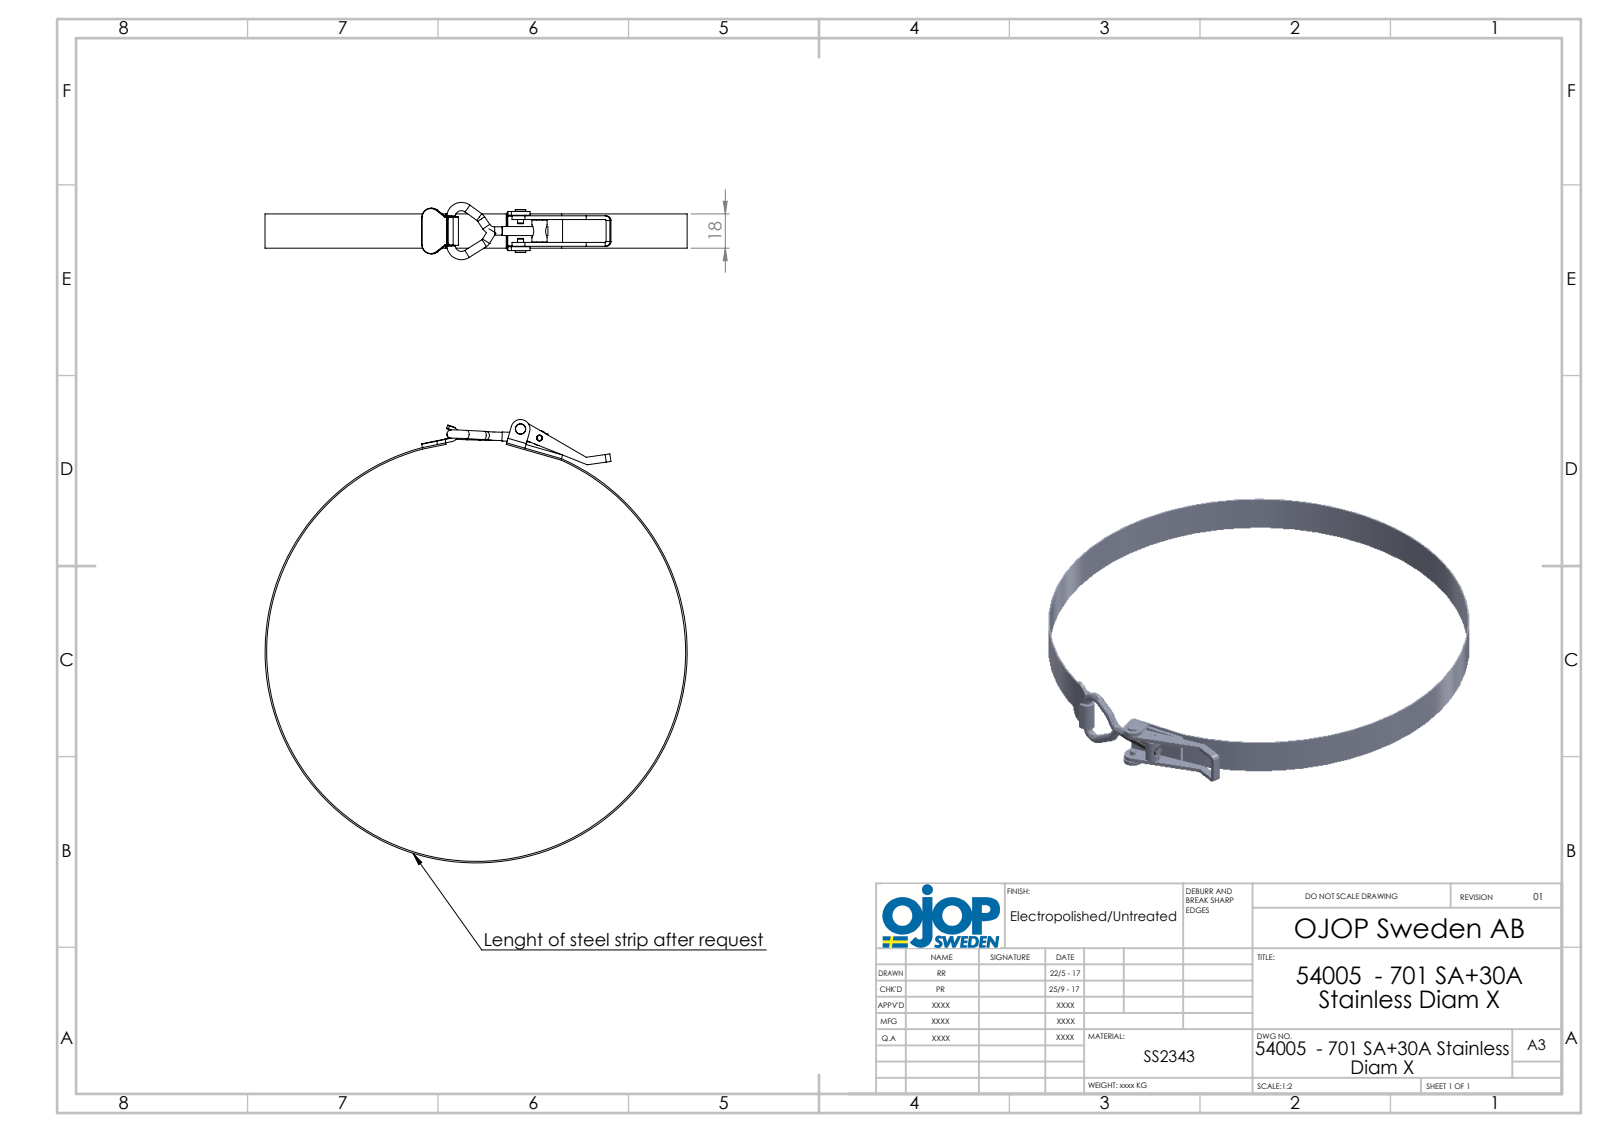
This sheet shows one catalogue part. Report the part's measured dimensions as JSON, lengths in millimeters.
{"part_name": "701 - SA; 54005 - 701 SA+30A RF Diam.220; 701 - Ansatsnit; 522601 - Striker 30 A (+5 more)", "step_written_by": "SolidWorks 2015 (AUTOMOTIVE_DESIGN)", "units": "millimeters", "bodies": {"solids": 8, "faces": 190, "planar": 68, "cylindrical": 82, "other": 40}, "overall_size": [232.69, 221.6, 30.09], "volume_mm3": 15446, "surface_area_mm2": 31876, "round_holes": [[3.2, 2], [4.3, 1], [4.5, 1], [220, 1]], "round_bosses_or_shafts": [[4.36, 5], [221.6, 1], [8, 1], [5.5, 1], [4.7, 1], [3.15, 1], [3, 1]], "partial_cylinders_radius": [[0.2, 12], [0.5, 4], [2.5, 4], [5, 3], [1, 2], [2, 1], [4, 1], [4.5, 1]], "face_to_face_distances": [2, 0.8, 2.8, 14, 1, 17, 3, 15, 18, 2.25], "hole_center_spacings": [11.03, 116.99, 119.19]}
